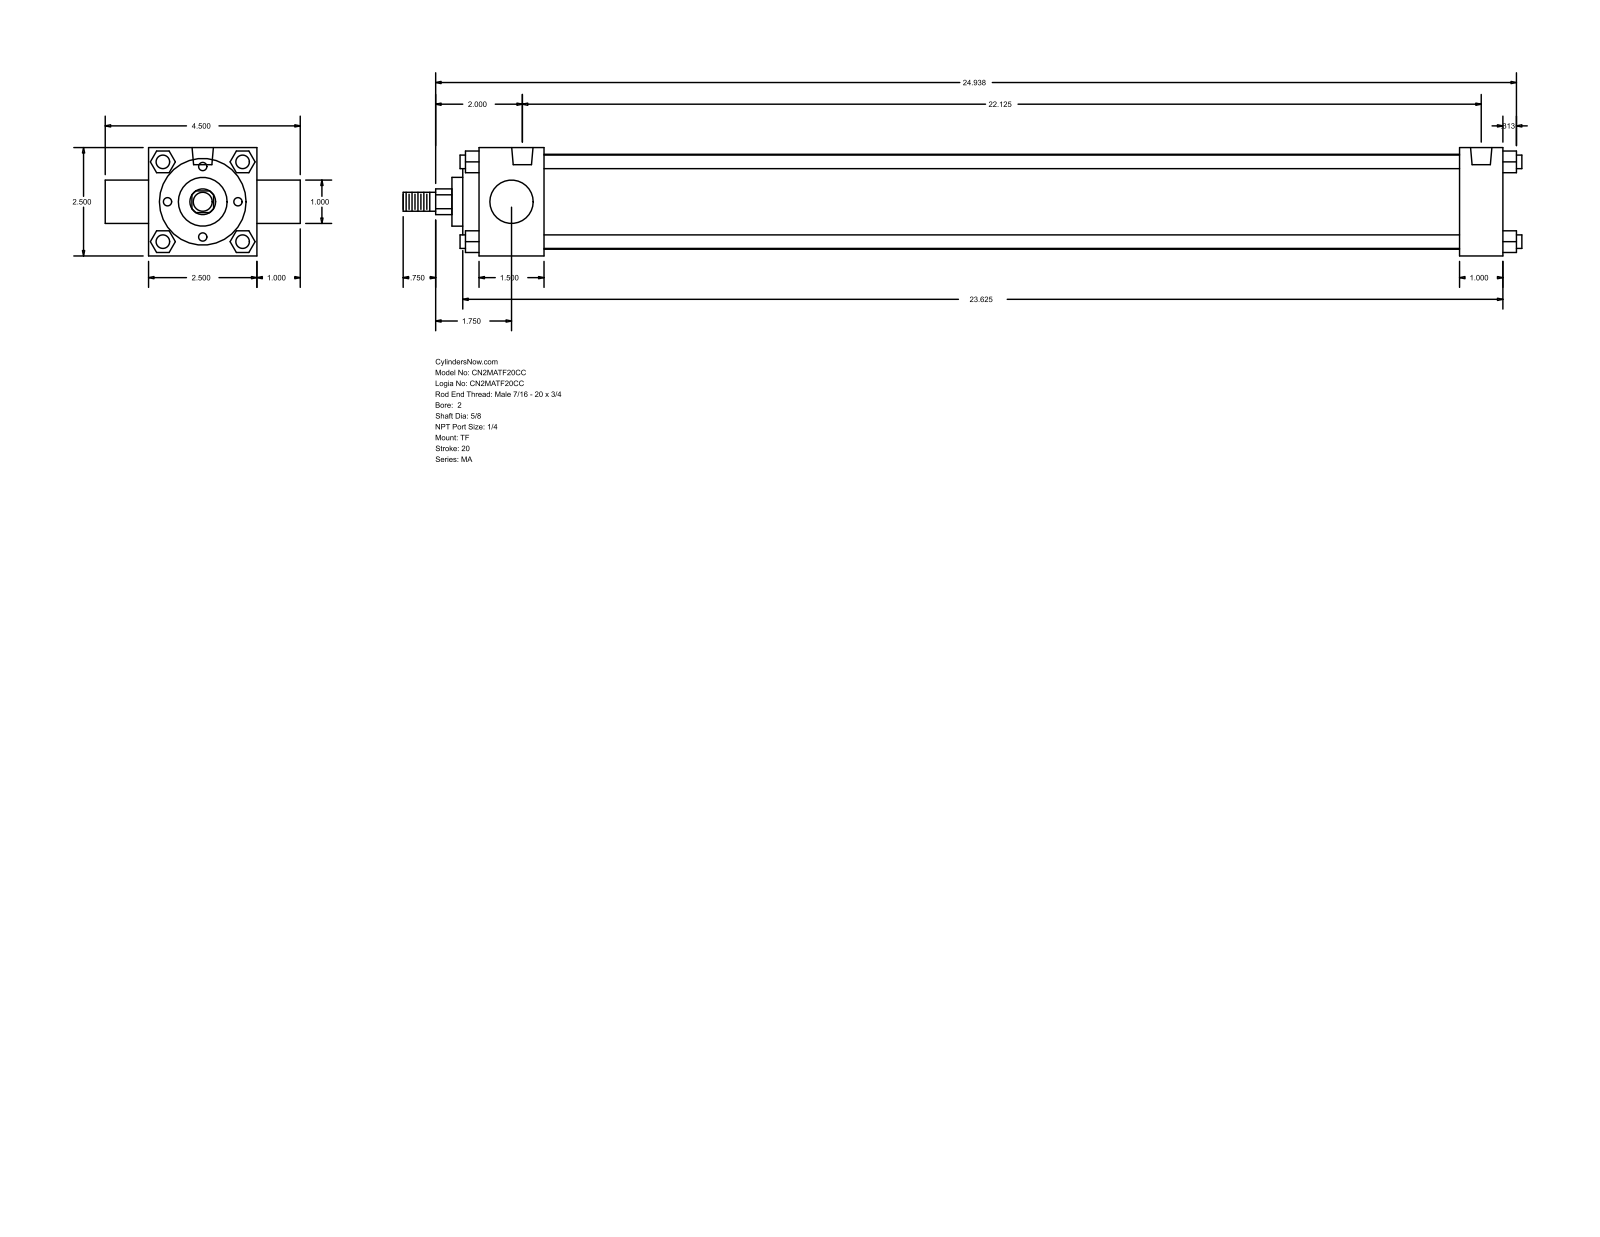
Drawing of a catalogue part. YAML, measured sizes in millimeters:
part_name: "MA_TF__0200_0.625"
step_written_by: "GSSL Pune (CONFIG_CONTROL_DESIGN)"
units: millimeters
bodies: {solids: 0, faces: 122, planar: 93, cylindrical: 29, other: 0}
overall_size: [655.64, 114.3, 63.5]
round_holes:
  - {diameter: 7.94, count: 3}
  - {diameter: 12.49, count: 2}
round_bosses_or_shafts:
  - {diameter: 7.94, count: 4}
  - {diameter: 55.63, count: 1}
  - {diameter: 50.8, count: 1}
  - {diameter: 28.57, count: 1}
  - {diameter: 25.4, count: 1}
  - {diameter: 15.88, count: 1}
  - {diameter: 11.11, count: 1}
partial_cylinders:
  - {radius: 7.54, count: 1}
face_to_face_distances: [63.5, 25.4, 38.1, 600.08, 12.7, 574.68, 536.58, 561.98, 9.52, 47.62]
hole_center_spacings: [561.97]
